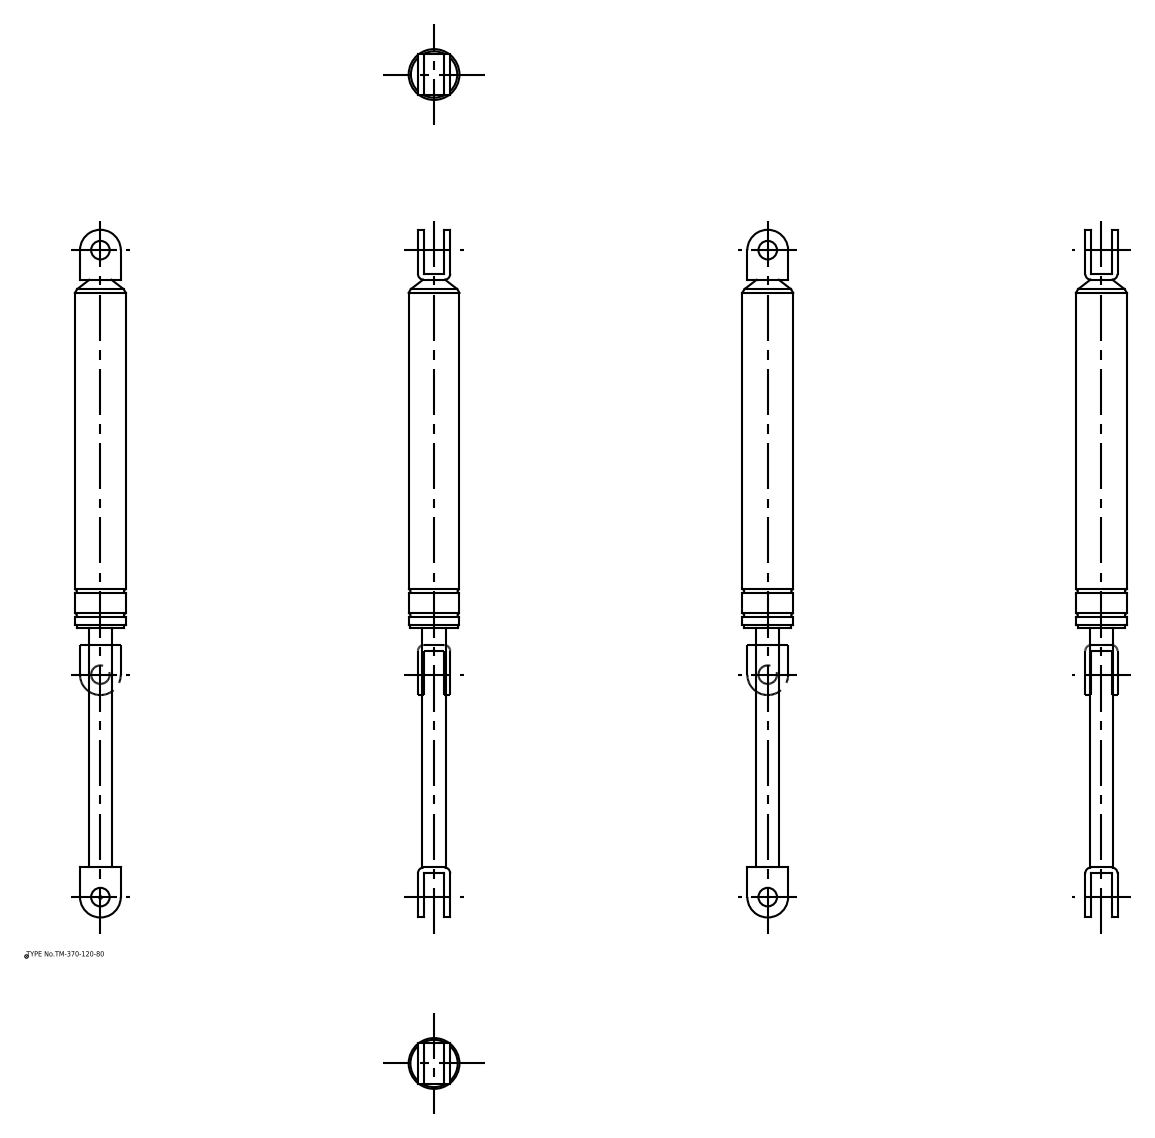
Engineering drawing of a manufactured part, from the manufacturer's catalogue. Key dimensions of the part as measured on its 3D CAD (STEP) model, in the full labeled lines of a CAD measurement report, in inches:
Part name (STEP PRODUCT): TM_370_120_80; TM_370_120_80_div
STEP written by: spGate 16.7.1 (AUTOMOTIVE_DESIGN)
Units: inches
Bodies: 2 solids, 64 faces (22 planar, 32 cylindrical, 10 other)
Overall size (bounding box): 14.606 × 1.11 × 1.11
Volume: 8.078 in³ · Surface area: 43.45 in²
Round holes (diameter × count): ⌀0.394 ×2
Round bosses / shafts (diameter × count): ⌀1.11 ×1, ⌀1.079 ×1, ⌀1.004 ×1, ⌀0.492 ×1
Partial cylindrical surfaces — rounded edges, fillets, slot ends (radius × count): R0.126 ×4, R0.433 ×2
Main face-to-face distances: 0.126, 0.559, 0.685, 0.433, 0.866, 12.606, 5.205, 12.732, 7.528, 7.402
Hole centre spacings: 13.74
